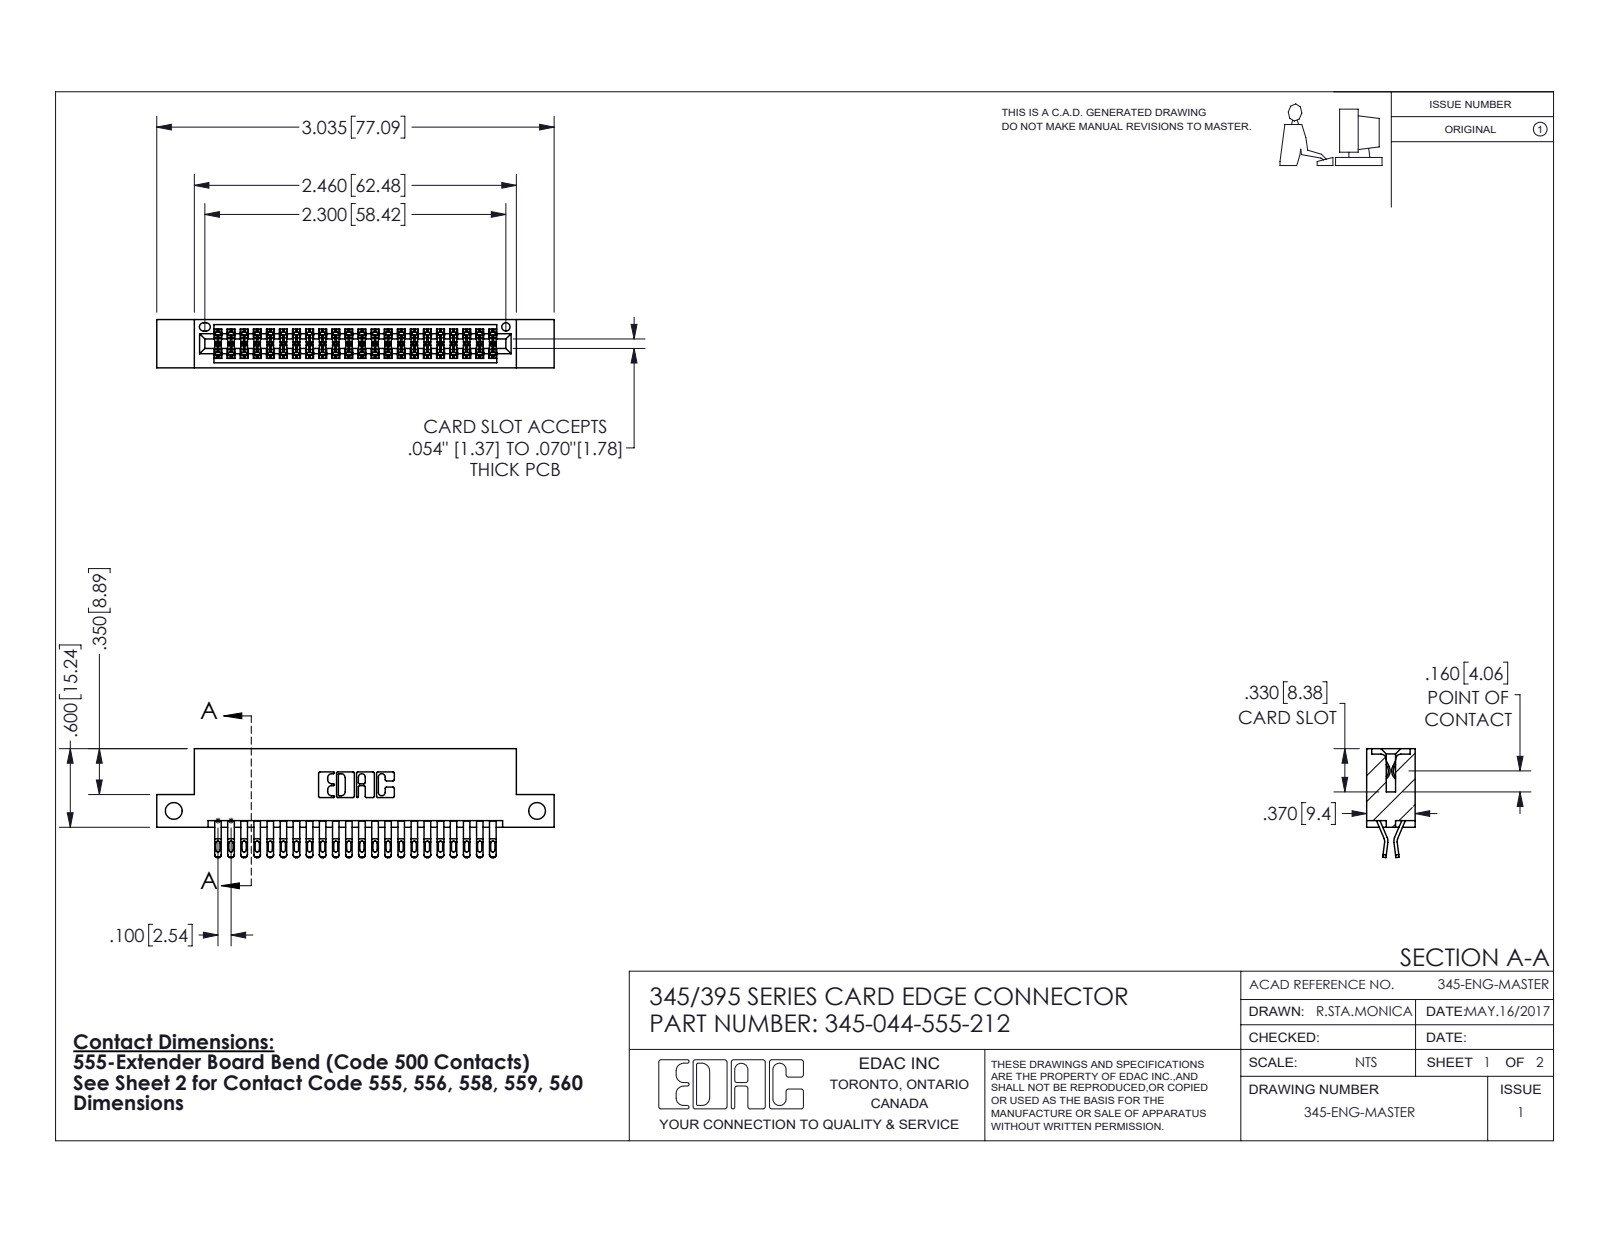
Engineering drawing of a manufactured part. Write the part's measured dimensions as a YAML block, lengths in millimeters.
part_name: "345-292-001_555 Tail; 345 Part_Flush Mounting Lugs - Side Mount; 345-044-555-212"
step_written_by: "SolidWorks 2016 (CONFIG_CONTROL_DESIGN)"
units: millimeters
bodies: {solids: 45, faces: 2590, planar: 1444, cylindrical: 1146, other: 0}
overall_size: [77.1, 21.1, 9.4]
volume: 7340
surface_area: 10770
round_holes:
  - {diameter: 3.3, count: 2}
  - {diameter: 1.6, count: 1}
partial_cylinders:
  - {radius: 0.4, count: 110}
  - {radius: 0.5, count: 88}
  - {radius: 0.2, count: 66}
  - {radius: 0.3, count: 22}
  - {radius: 0.2, count: 6}
  - {radius: 0.8, count: 6}
  - {radius: 0.7, count: 3}
  - {radius: 0.3, count: 2}
face_to_face_distances: [7.6, 1.8, 5.1, 9.4, 0.6, 2.5, 6.9, 5.7, 4.4, 3.8]
hole_center_spacings: [70.5]
